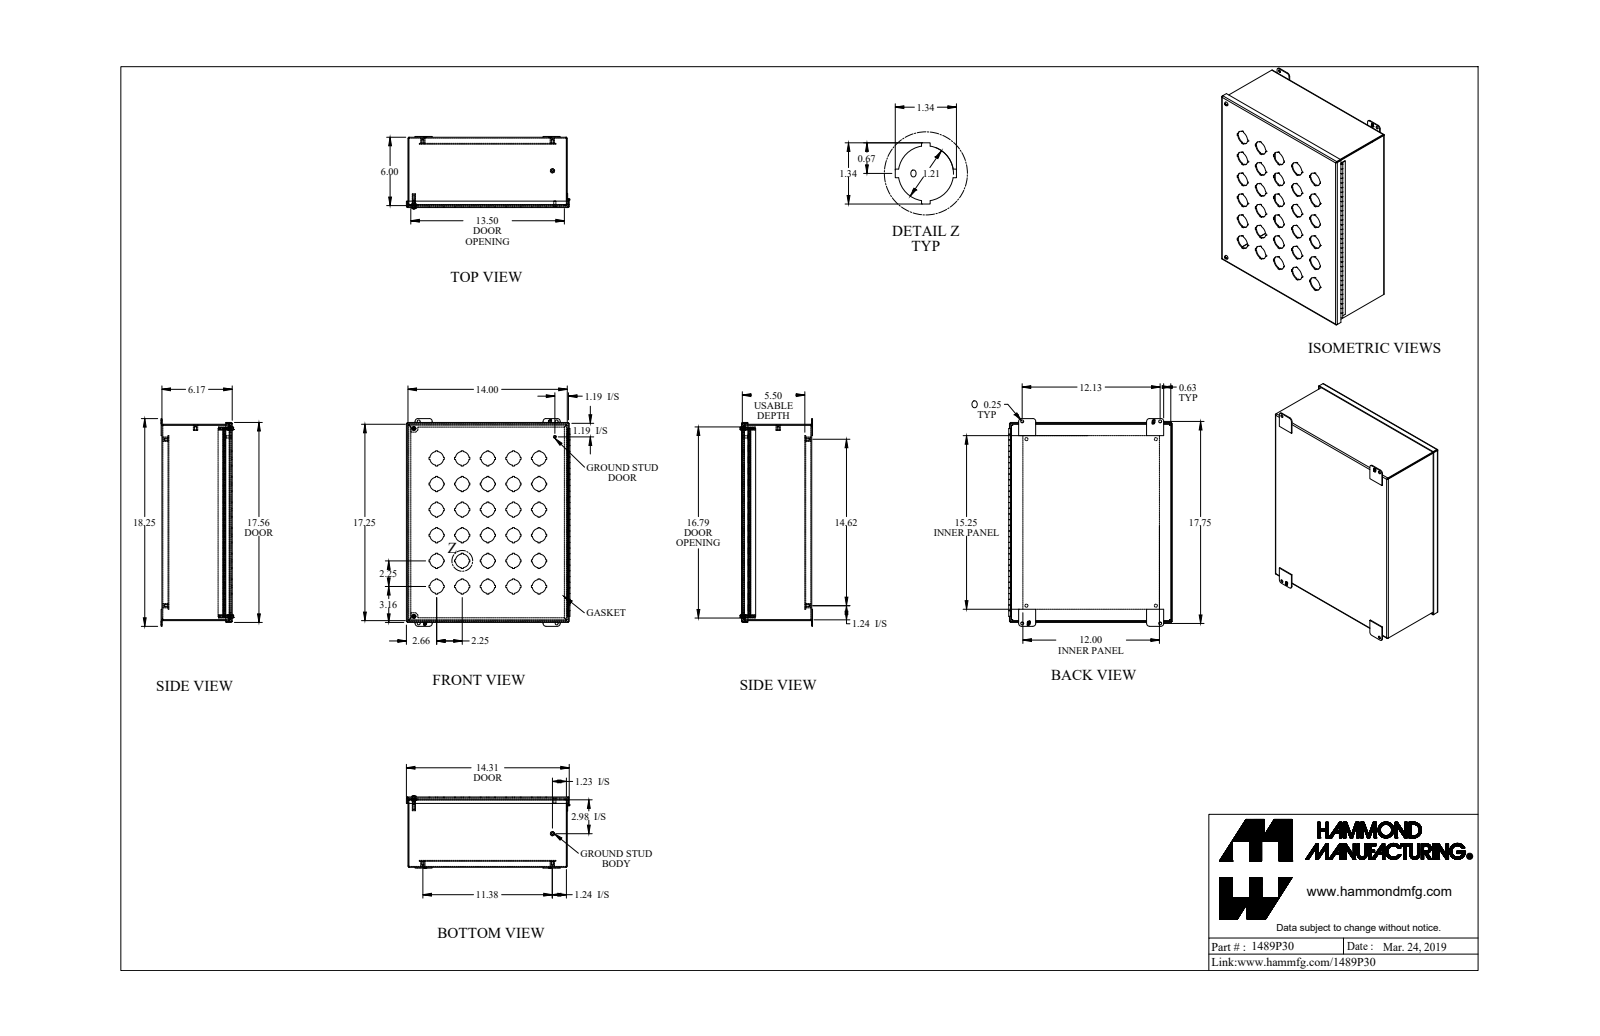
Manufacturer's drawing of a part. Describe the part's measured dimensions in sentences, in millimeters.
The part is named "1489P30_Default". Its 3-D file was written by "SolidWorks 2019 (CONFIG_CONTROL_DESIGN)". It is 21 solids with 1277 faces: 894 planar, 325 cylindrical and 58 other. Overall it measures 463.6 by 365.1 by 161.8 millimeters. Its volume is 1 401 000 cubic millimeters and its surface area 1 486 000 square millimeters. Round holes: 30 of diameter 30.7, 6 of diameter 6.4, 5 of diameter 4, 4 of diameter 6.7, 2 of diameter 4, 2 of diameter 10.3. Round bosses or shafts: 5 of diameter 9.5, 2 of diameter 9.9, 2 of diameter 7, 2 of diameter 4.8, 2 of diameter 3.8, 1 of diameter 6.4, 1 of diameter 4.8, 1 of diameter 4.4. Partial cylindrical surfaces (rounded edges, fillets, slot ends): 12 of radius 0.9, 12 of radius 2.7, 8 of radius 6.4, 2 of radius 4.1, 2 of radius 4.3. The main face-to-face distances are 1.8, 154.9, 141.4, 13.5, 153.1, 156.8, 353.8, 15.3, 143.3, 11.7. The hole center spacings are 127.8, 57.2, 180.7, 80.8, 114.3, 206.1, 171.5, 161.6.
